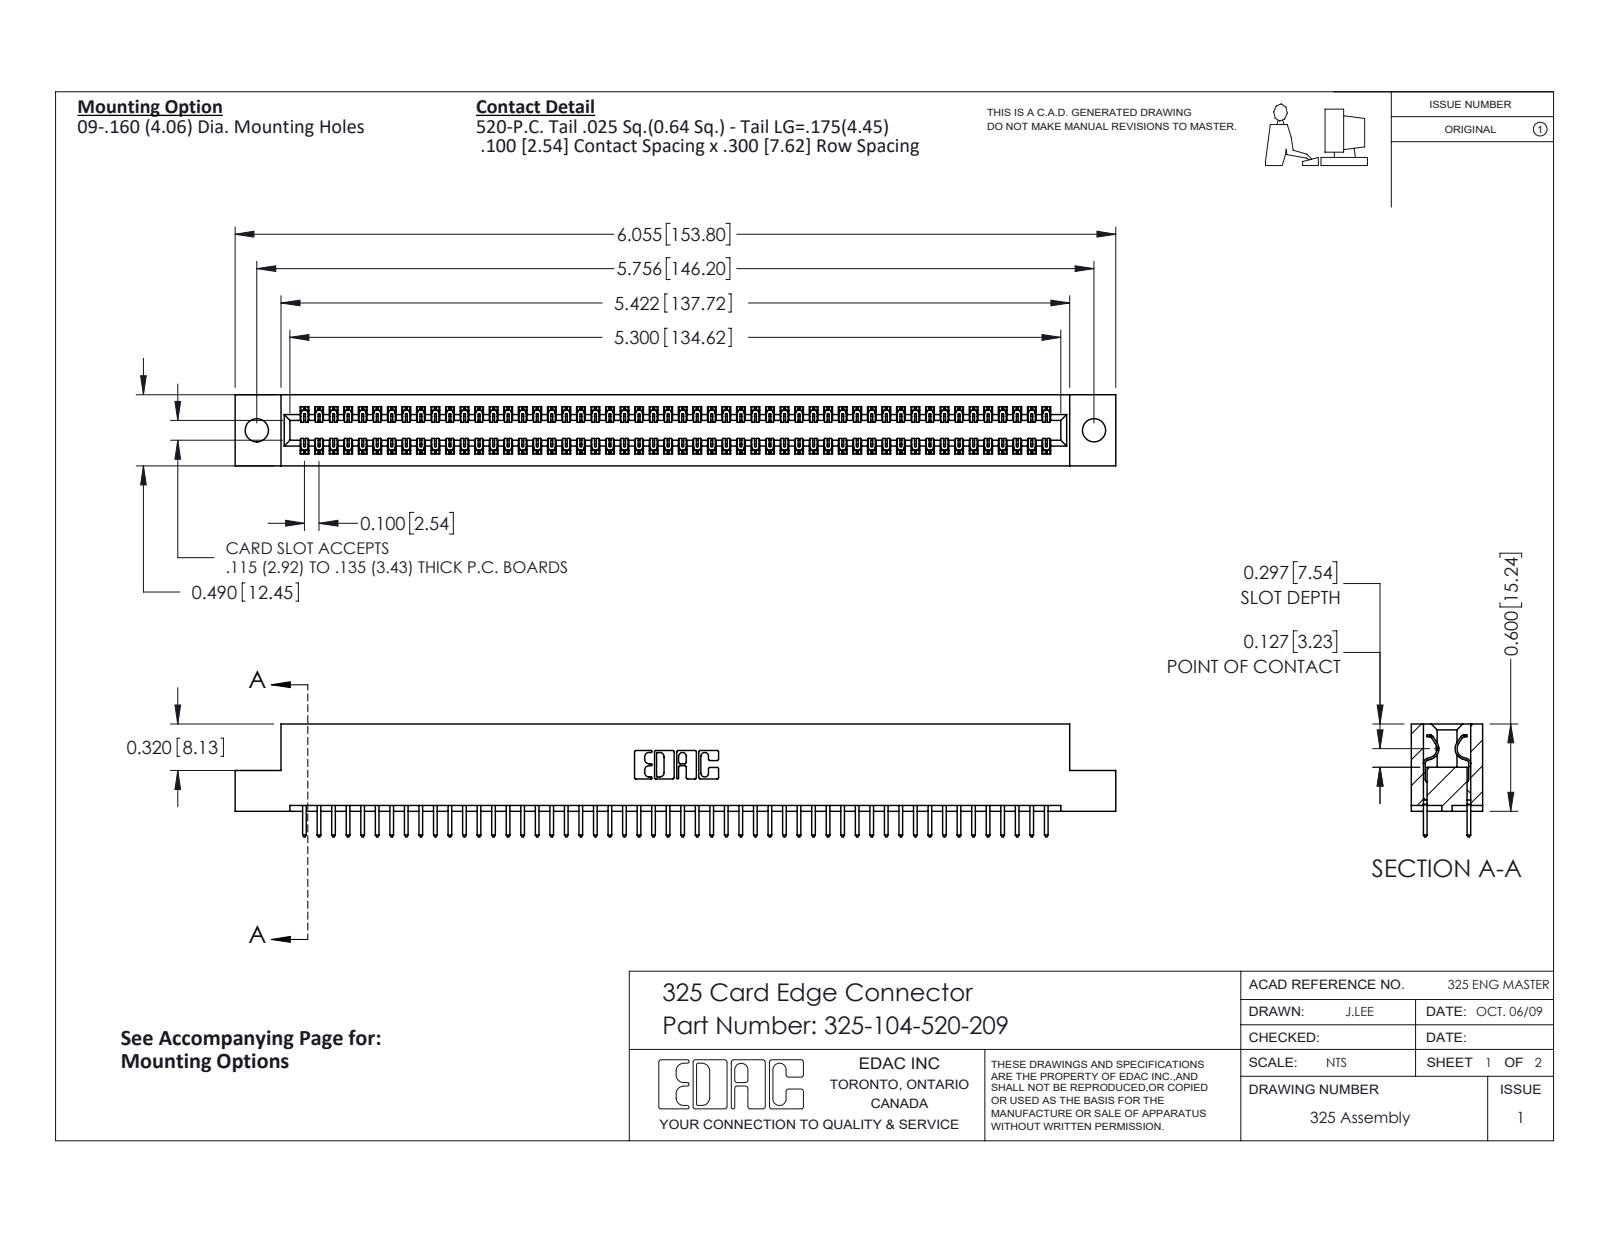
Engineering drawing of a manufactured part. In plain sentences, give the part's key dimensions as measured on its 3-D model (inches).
The part is named "325-292-001_325-293-120; 325 Part_.160 TH; 325-104-520-209". Its 3-D file was written by "SolidWorks 2016 (CONFIG_CONTROL_DESIGN)". It is 105 solids with 5522 faces: 3814 planar, 1708 cylindrical and 0 other. Overall it measures 6.055 by 0.775 by 0.49 inches. Its volume is 1.202 cubic inches and its surface area 36.87 square inches. Round holes: 2 of diameter 0.16. Partial cylindrical surfaces (rounded edges, fillets, slot ends): 156 of radius 0.006, 104 of radius 0.01, 22 of radius 0.01, 6 of radius 0.007, 6 of radius 0.031, 3 of radius 0.026, 2 of radius 0.014, 2 of radius 0.022. The main face-to-face distances are 0.083, 0.407, 0.3, 0.49, 0.107, 0.383, 0.025, 0.325, 0.275, 0.56. The hole center spacings are 5.756.
